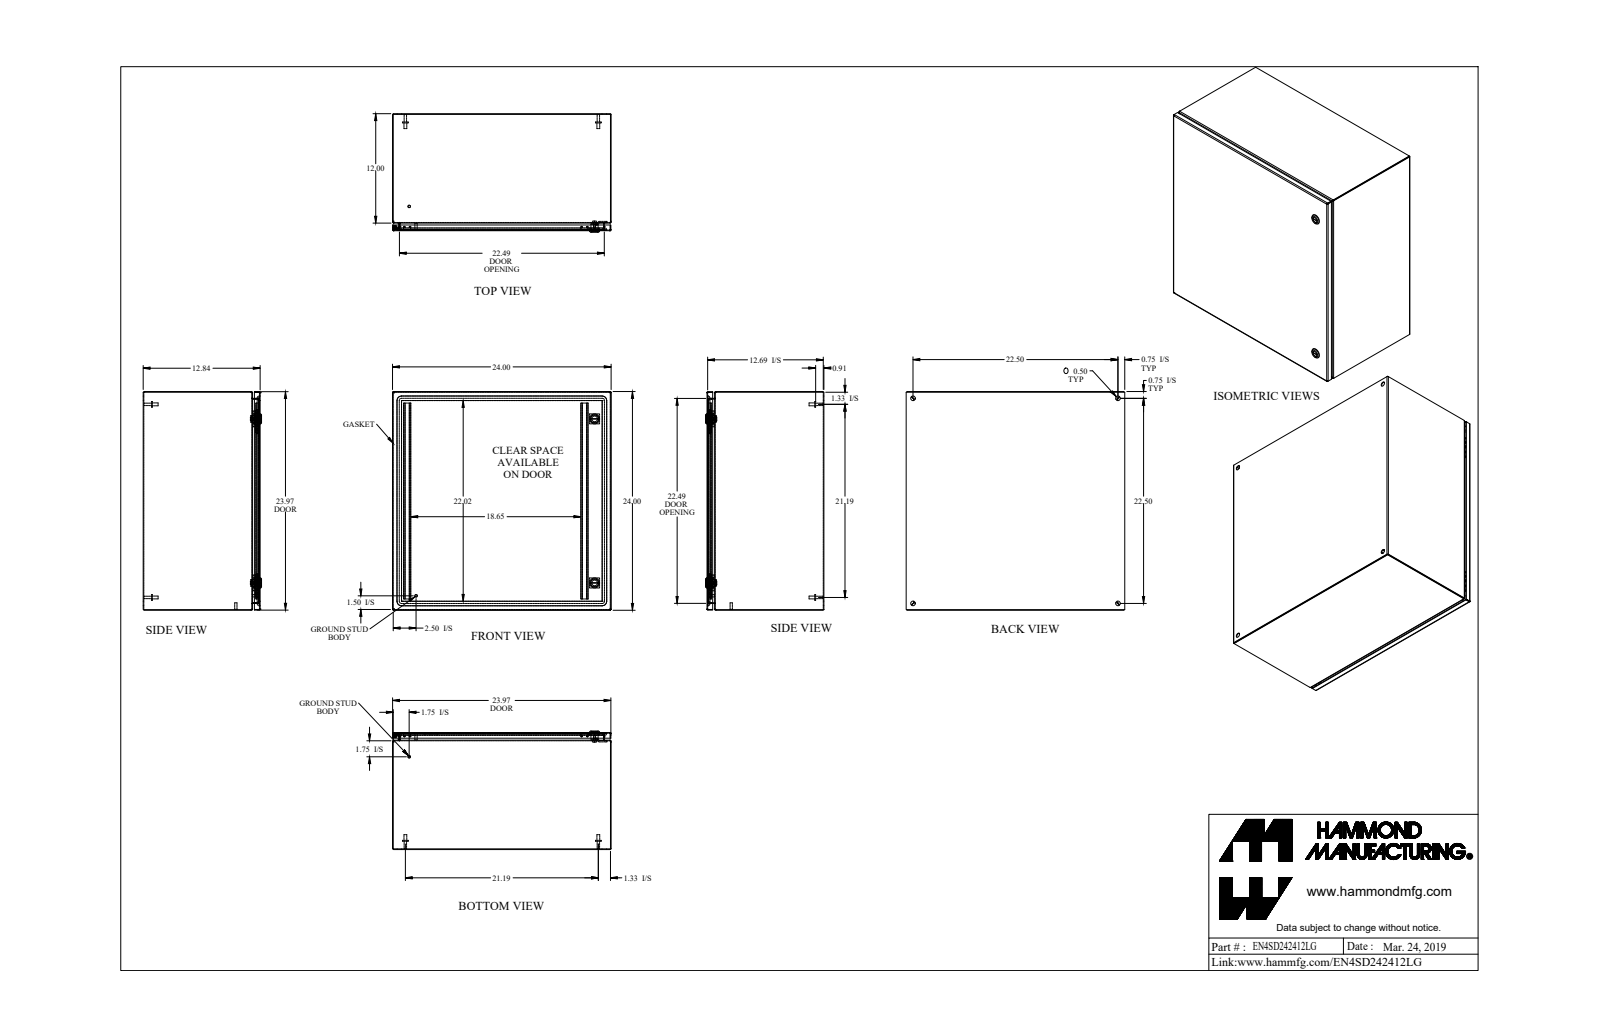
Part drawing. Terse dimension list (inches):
name: EN4SD242412LG
written by: SolidWorks 2019 (AUTOMOTIVE_DESIGN)
unit: in
bodies: 29 solids, 736 faces (363 planar, 245 cylindrical, 128 other)
size: 24 × 24 × 12.997
volume: 191.3 in³; area: 5 360 in²
holes: 4× ⌀0.5, 2× ⌀0.232, 2× ⌀0.625, 2× ⌀0.785, 1× ⌀0.172, 1× ⌀0.24, 1× ⌀0.242
bosses: 4× ⌀0.625, 4× ⌀0.313, 4× ⌀0.27, 2× ⌀1.1, 2× ⌀0.525, 2× ⌀0.281, 2× ⌀0.25, 1× ⌀0.455
rounds: 14× R0.036, 14× R0.108, 12× R0.043, 12× R0.081, 12× R0.312, 8× R0.1, 4× R0.006, 4× R0.062
face distances: 0.072, 12.765, 23.928, 12.693, 23.856, 12.837, 24, 0.837, 11.928, 0.75
hole spacings: 22.5, 31.82, 2.493, 2.494, 17.999, 20.277, 20.278, 21.544
